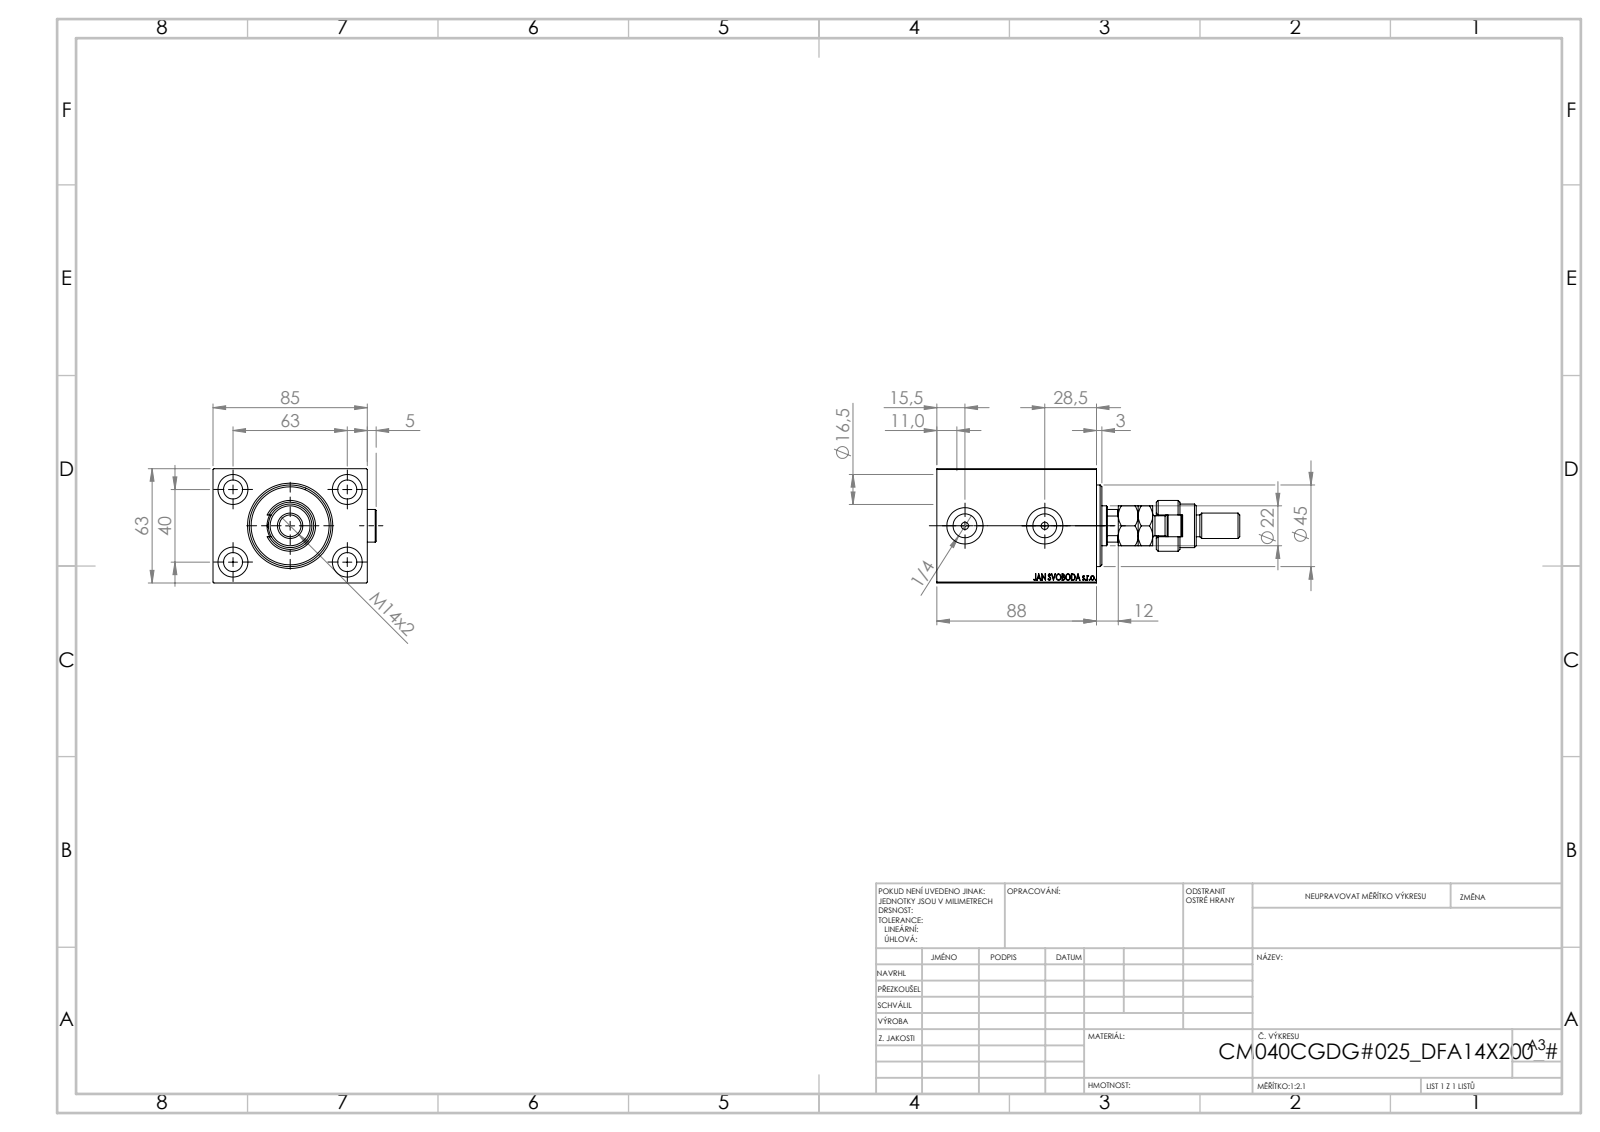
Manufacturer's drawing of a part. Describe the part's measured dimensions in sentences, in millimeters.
The part is named "V450CM_C_VCP; FEMALE_PART_FOR_DFA; Zatka_OIL_PORT; V450CM_VC_B (+2 more)". Its 3-D file was written by "SolidWorks 2019 (CONFIG_CONTROL_DESIGN)". It is 7 solids with 1001 faces: 470 planar, 89 cylindrical and 442 other. Overall it measures 167 by 89.9 by 63 millimeters. Its volume is 429 043 cubic millimeters and its surface area 88 099 square millimeters. Round holes: 4 of diameter 10.5, 4 of diameter 16.5, 2 of diameter 4, 2 of diameter 13.16, 2 of diameter 20, 1 of diameter 12.5, 1 of diameter 22, 1 of diameter 25.5, 1 of diameter 40, 1 of diameter 42, 1 of diameter 45. Round bosses or shafts: 3 of diameter 18, 1 of diameter 28, 1 of diameter 24, 1 of diameter 14, 1 of diameter 12, 1 of diameter 11. Partial cylindrical surfaces (rounded edges, fillets, slot ends): 1 of radius 9.75, 1 of radius 10.5. The main face-to-face distances are 63, 85, 12, 76, 88, 40, 84.9, 3, 15, 64. The hole center spacings are 37.31, 40, 63, 74.63, 44.
